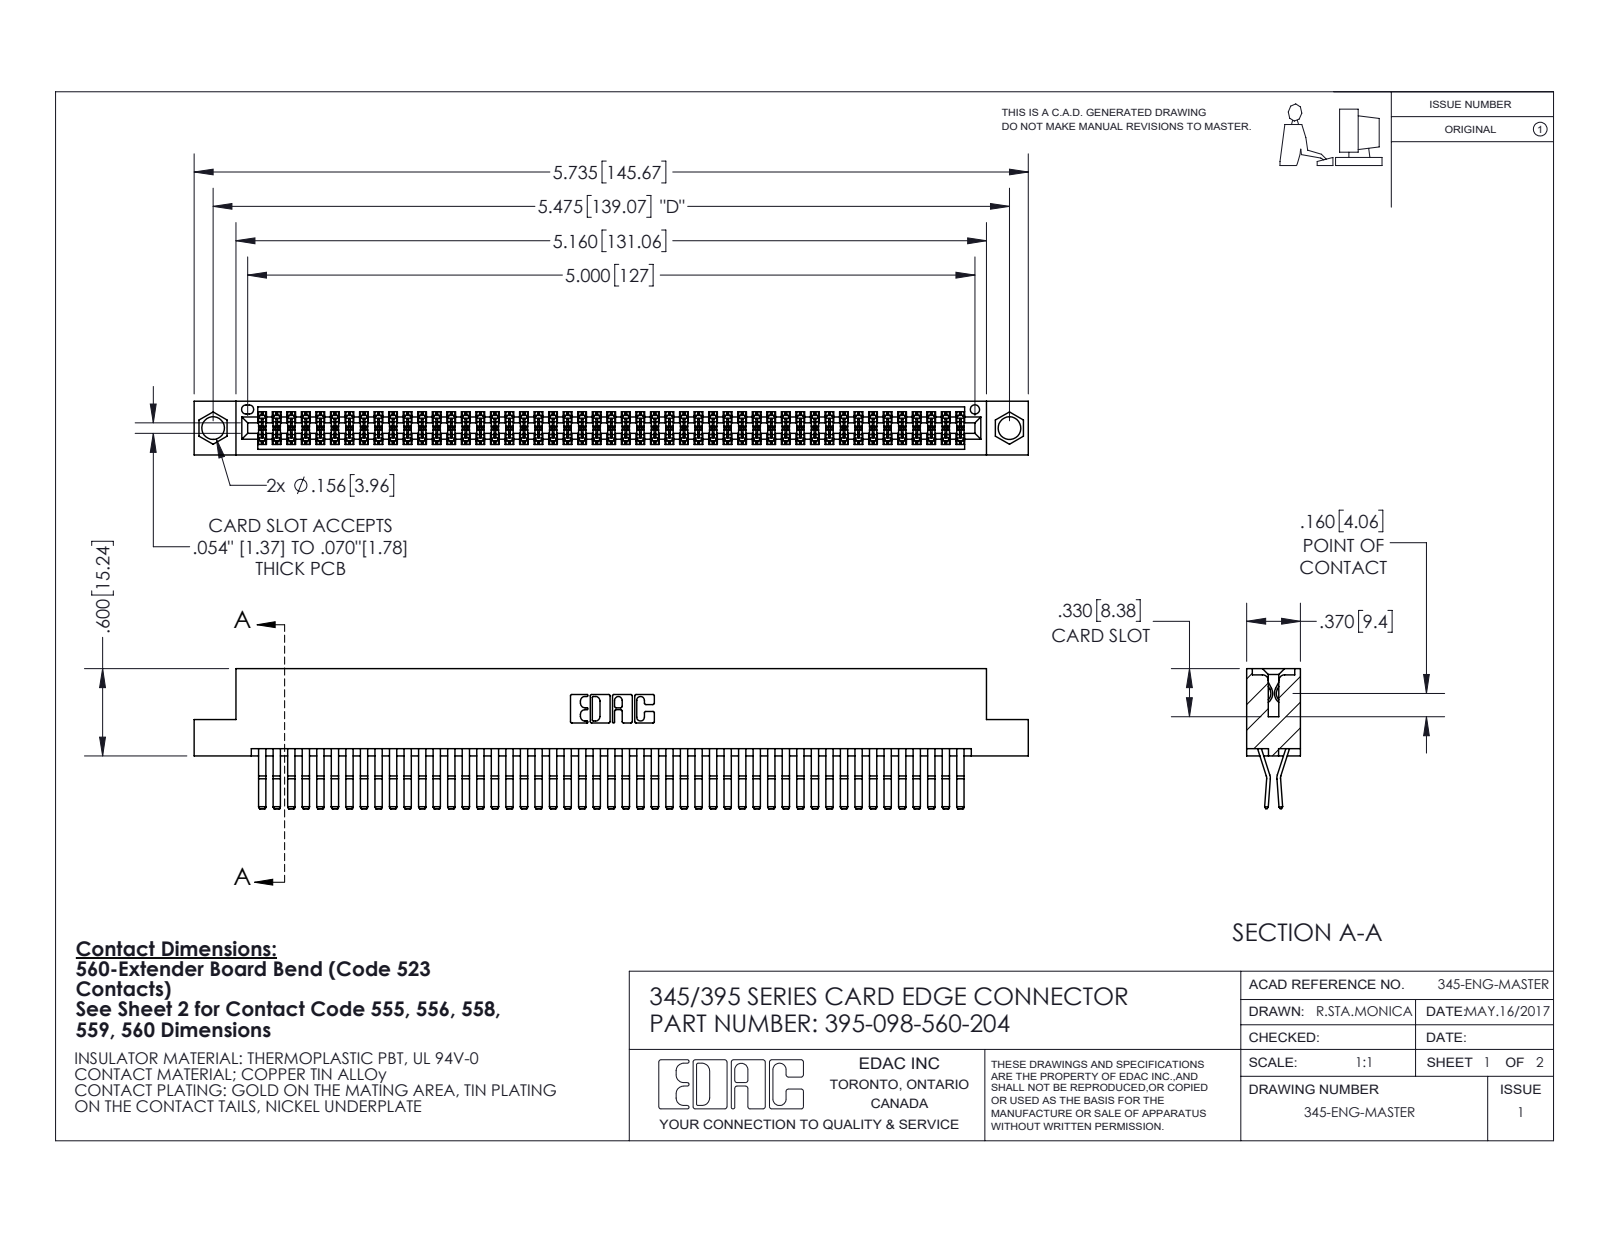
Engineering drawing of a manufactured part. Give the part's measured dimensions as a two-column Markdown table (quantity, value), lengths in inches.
| quantity | value |
| --- | --- |
| part name | 395-098-560-204; 345-292-001_560 Tail; 345 Part_Flush Mounting Lugs - 0.156 Dia-TI |
| STEP written by | SolidWorks 2020 (CONFIG_CONTROL_DESIGN) |
| units | inches |
| bodies | 99 solids, 5236 faces (3328 planar, 1908 cylindrical, 0 other) |
| overall size | 5.735 × 0.962 × 0.37 |
| volume | 0.9 in³ |
| surface area | 36.34 in² |
| round holes (diameter × count) | 0.156 × 2, 0.064 × 1 |
| partial cylindrical surfaces (radius × count) | 0.006 × 196, 0.01 × 22, 0.007 × 6, 0.031 × 6, 0.026 × 3, 0.01 × 2, 0.014 × 2, 0.019 × 2 |
| main face-to-face distances | 0.025, 0.298, 0.072, 0.2, 0.37, 0.098, 0.272, 0.225, 0.175, 0.149 |
| hole center spacings | 0.27, 5.239, 5.475 |
